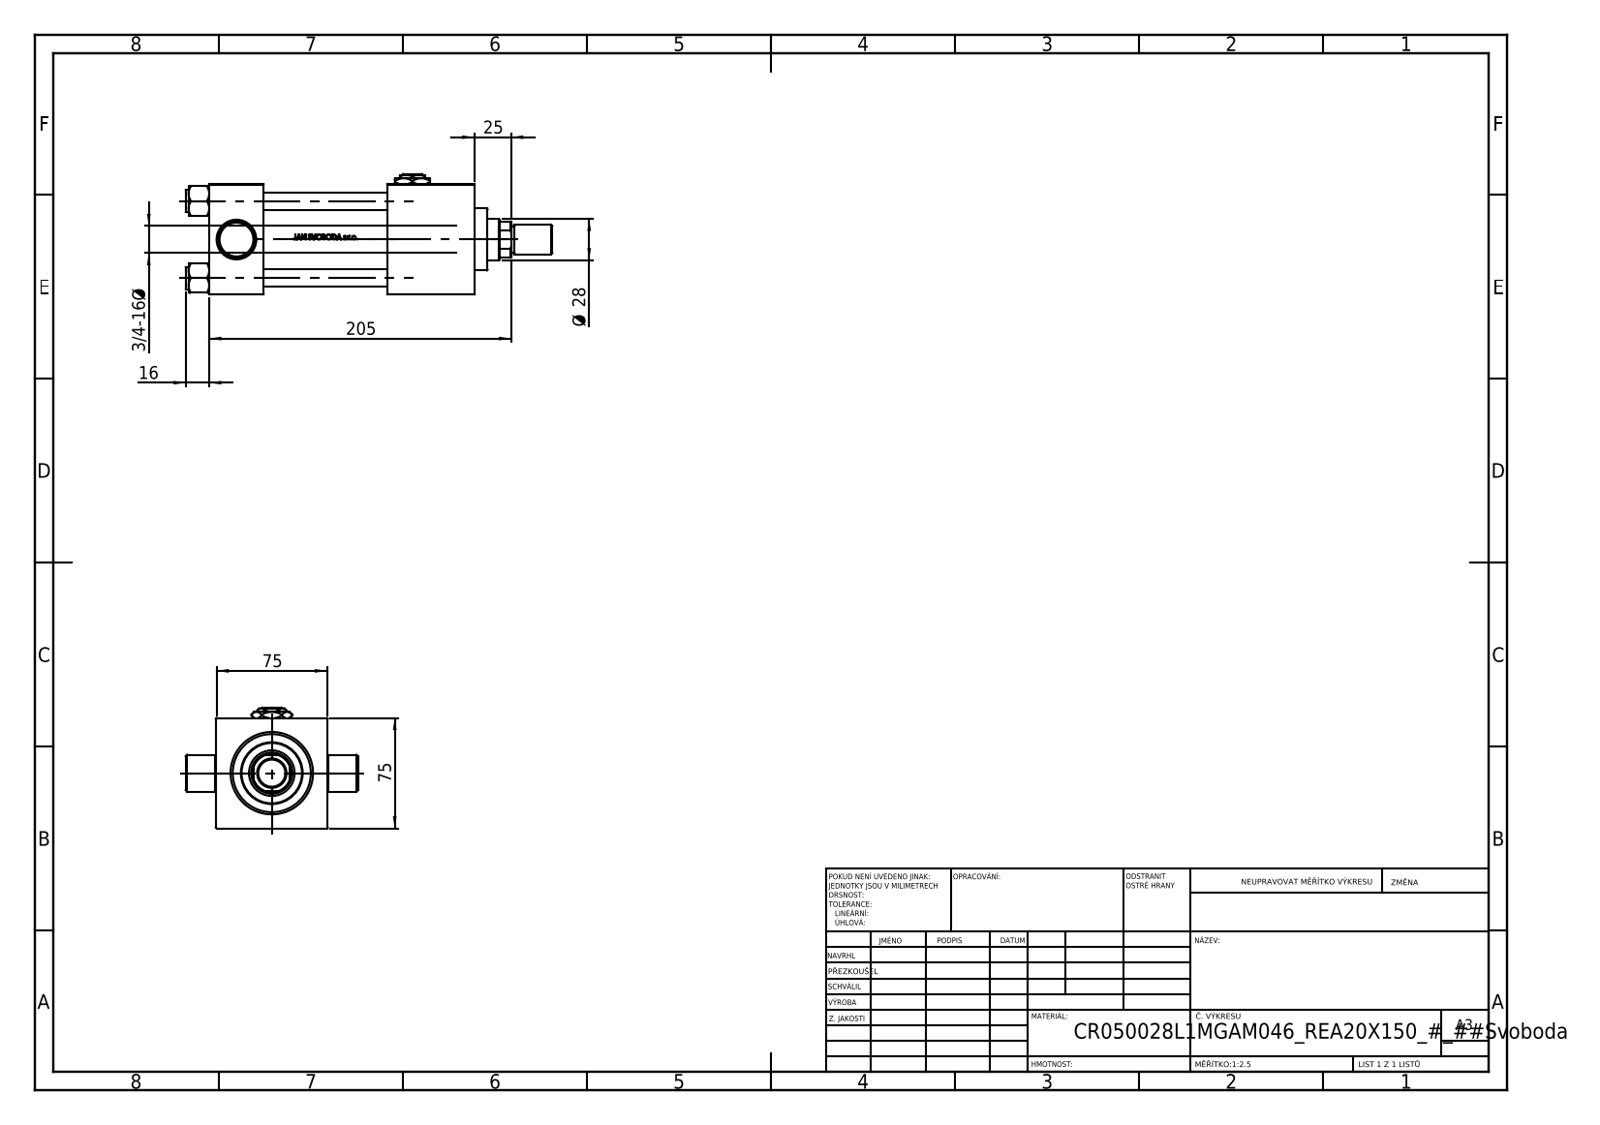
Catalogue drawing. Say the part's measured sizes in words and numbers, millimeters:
The part is named "V215CR_L_Body; V215CR_VCP_L; ROD_END_AH; V215CR_L_TYCINKA (+3 more)". Its 3-D file was written by "SolidWorks 2019 (CONFIG_CONTROL_DESIGN)". It is 13 solids with 1133 faces: 455 planar, 128 cylindrical and 550 other. Overall it measures 249 by 117 by 82 millimeters. Its volume is 748 381 cubic millimeters and its surface area 168 485 square millimeters. Round holes: 4 of diameter 12, 2 of diameter 7, 2 of diameter 20.96, 2 of diameter 30, 1 of diameter 18.5, 1 of diameter 28, 1 of diameter 31, 1 of diameter 41, 1 of diameter 50, 1 of diameter 53. Round bosses or shafts: 4 of diameter 15, 1 of diameter 56, 1 of diameter 42, 1 of diameter 25, 1 of diameter 20, 1 of diameter 18. Partial cylindrical surfaces (rounded edges, fillets, slot ends): 1 of radius 13.5. The main face-to-face distances are 75, 37, 0.5, 76, 75.5, 59, 180, 143, 84, 121. The hole center spacings are 36.98, 52.3, 73.96, 119.5.
